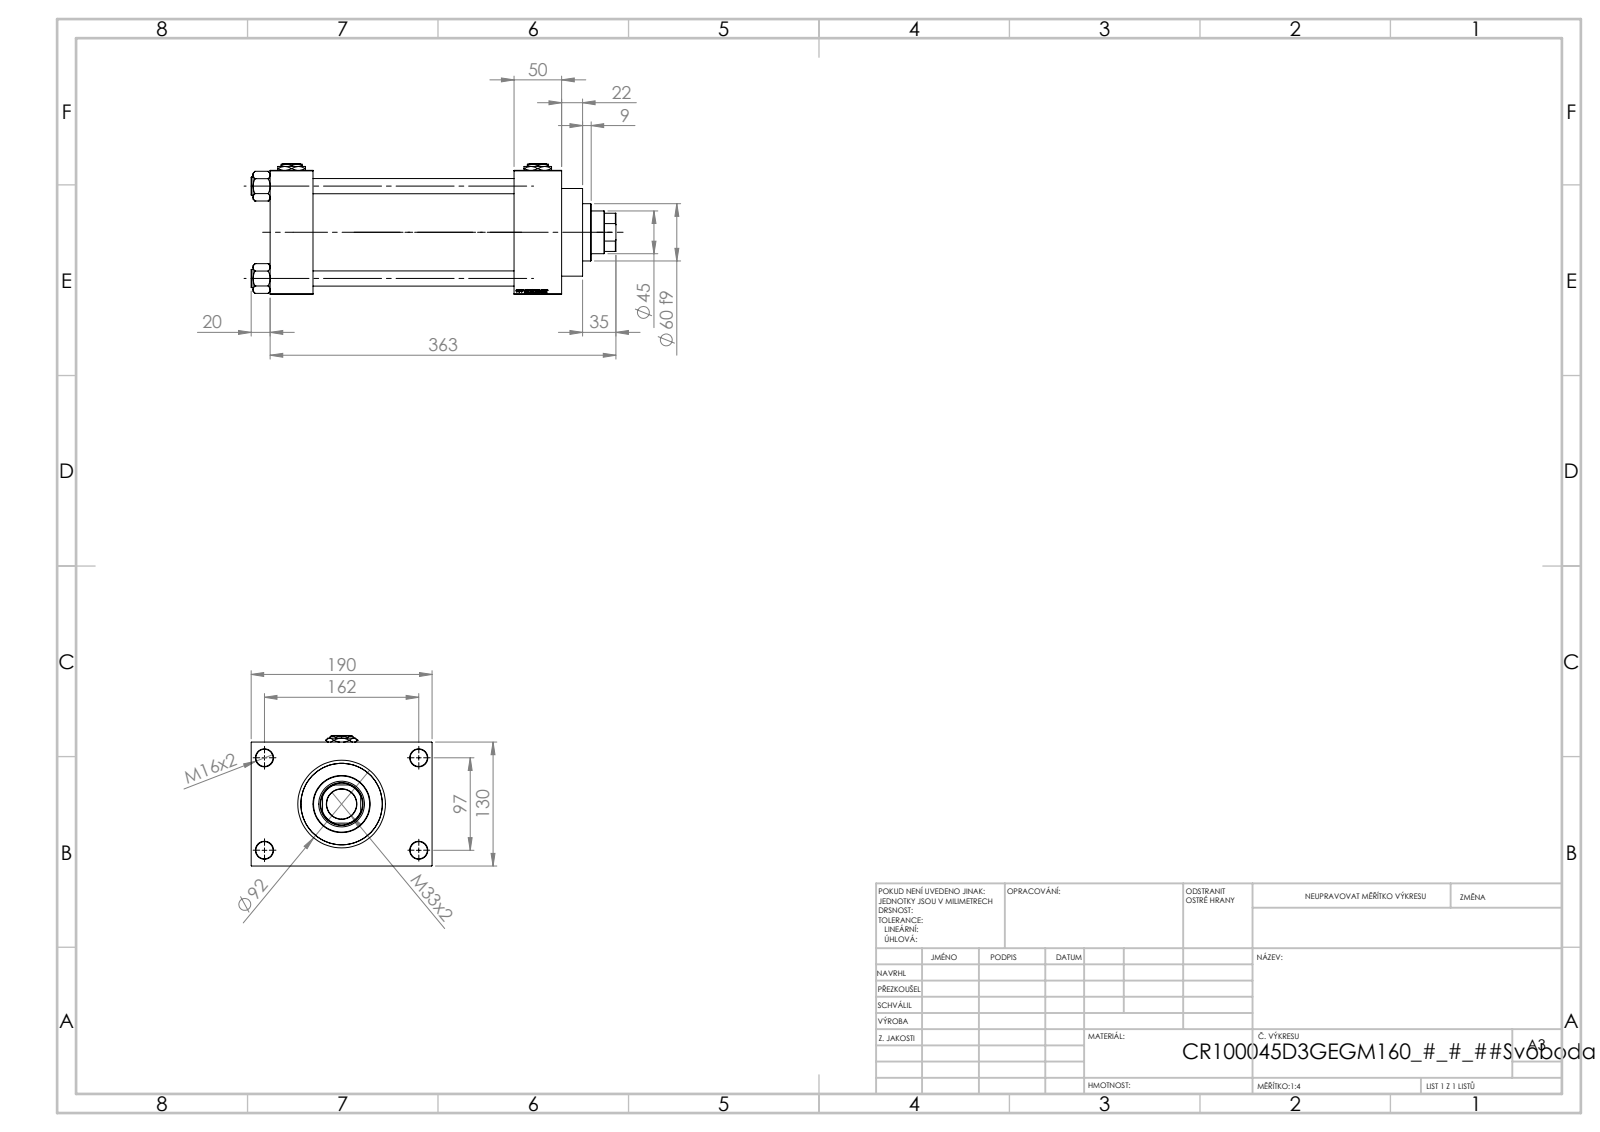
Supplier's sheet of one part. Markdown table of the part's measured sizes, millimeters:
| quantity | value |
| --- | --- |
| part name | NUT_M5_D; V215_VC_A; V215CR_D_TYCINKA; V215CR_D_Body (+2 more) |
| STEP written by | SolidWorks 2019 (CONFIG_CONTROL_DESIGN) |
| units | millimeters |
| bodies | 13 solids, 1253 faces (593 planar, 100 cylindrical, 560 other) |
| overall size | 383 × 190 × 137 |
| volume | 3 064 000 mm³ |
| surface area | 497 856 mm² |
| round holes (diameter × count) | 16 × 4, 18 × 4, 7 × 2, 26.44 × 2, 35 × 2, 31.5 × 1, 45 × 1, 48 × 1, 76 × 1, 85.5 × 1, 100 × 1 |
| round bosses / shafts (diameter × count) | 19 × 4, 106 × 1, 92 × 1, 60 × 1 |
| partial cylindrical surfaces (radius × count) | 22 × 1 |
| main face-to-face distances | 130, 45, 160, 256, 211, 306, 261, 50, 30, 190 |
| hole center spacings | 32.55, 68.52, 94.41, 96.9, 102.27, 129.45, 161.73, 97 |
